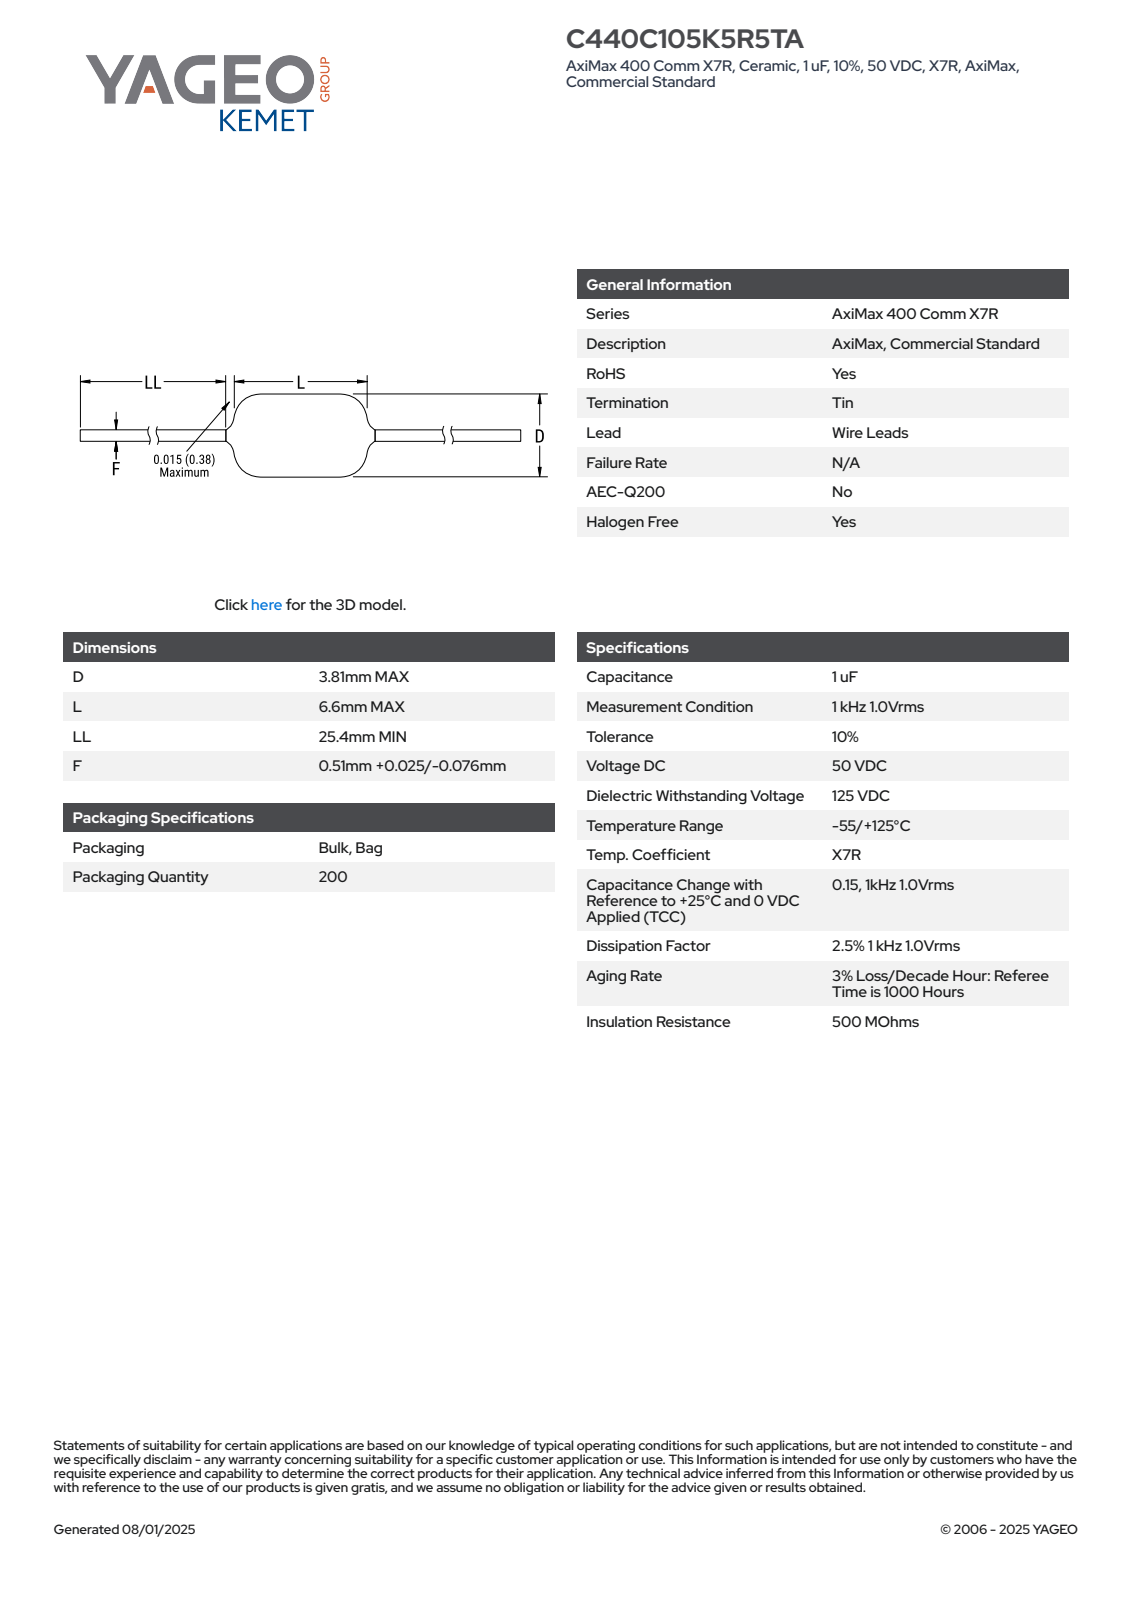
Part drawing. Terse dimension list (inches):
name: CCA_ACST_C440_D3.81L6.6LL25.4F0.535
written by: SolidWorks 2014 (AUTOMOTIVE_DESIGN)
unit: in
bodies: 1 solid, 74 faces (26 planar, 9 cylindrical, 39 other)
size: 2.29 × 0.15 × 0.15
volume: 0.005 in³; area: 0.279 in²
bosses: 1× ⌀0.15, 1× ⌀0.021
rounds: 1× R0.075
face distances: 0.26, 1.015, 1.275, 2.29
